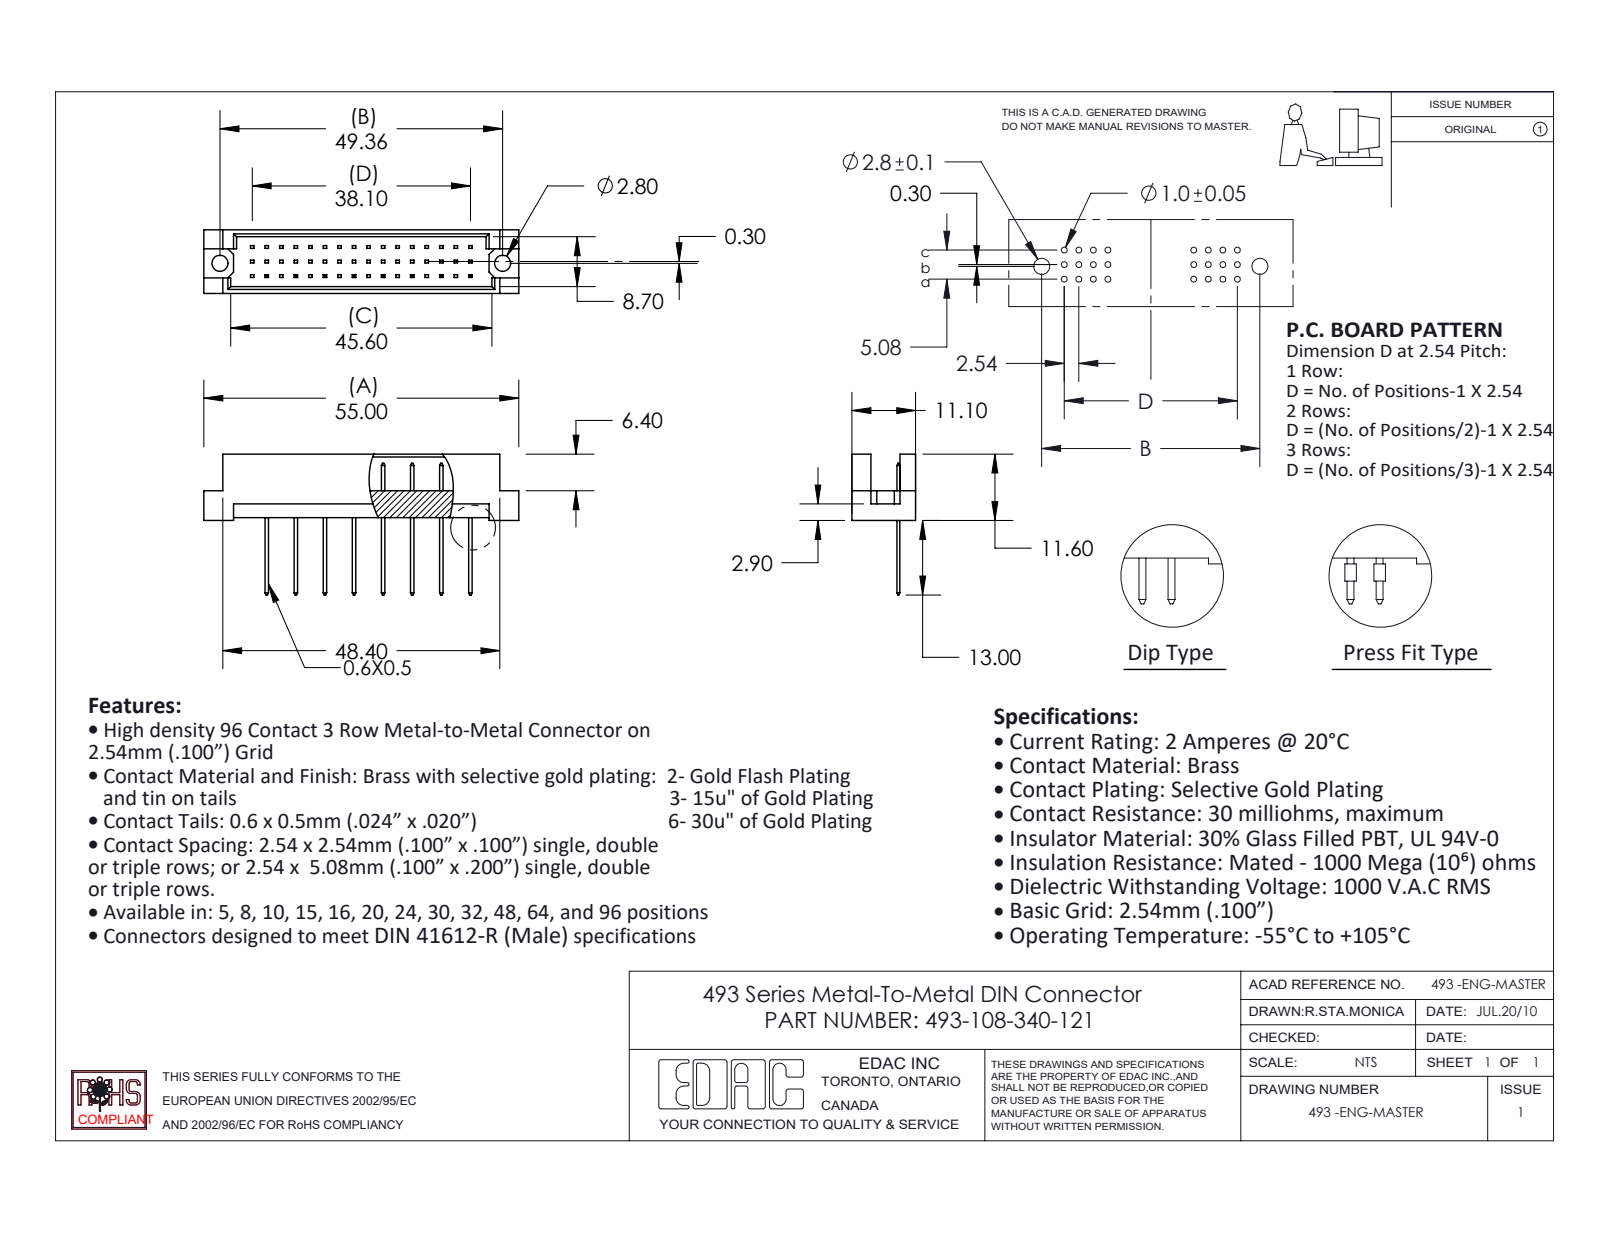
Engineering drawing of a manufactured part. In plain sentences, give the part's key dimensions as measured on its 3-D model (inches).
The part is named "493-290_40; 493-108-340-122; 493 Part_48". Its 3-D file was written by "SolidWorks 2020 (CONFIG_CONTROL_DESIGN)". It is 9 solids with 356 faces: 352 planar, 4 cylindrical and 0 other. Overall it measures 2.165 by 0.969 by 0.437 inches. Its volume is 0.203 cubic inches and its surface area 6.445 square inches. Round holes: 2 of diameter 0.11. The main face-to-face distances are 0.047, 0.39, 0.437, 0.343, 0.185, 0.02, 0.2, 0.109, 0.328, 0.061. The hole center spacings are 1.943.
